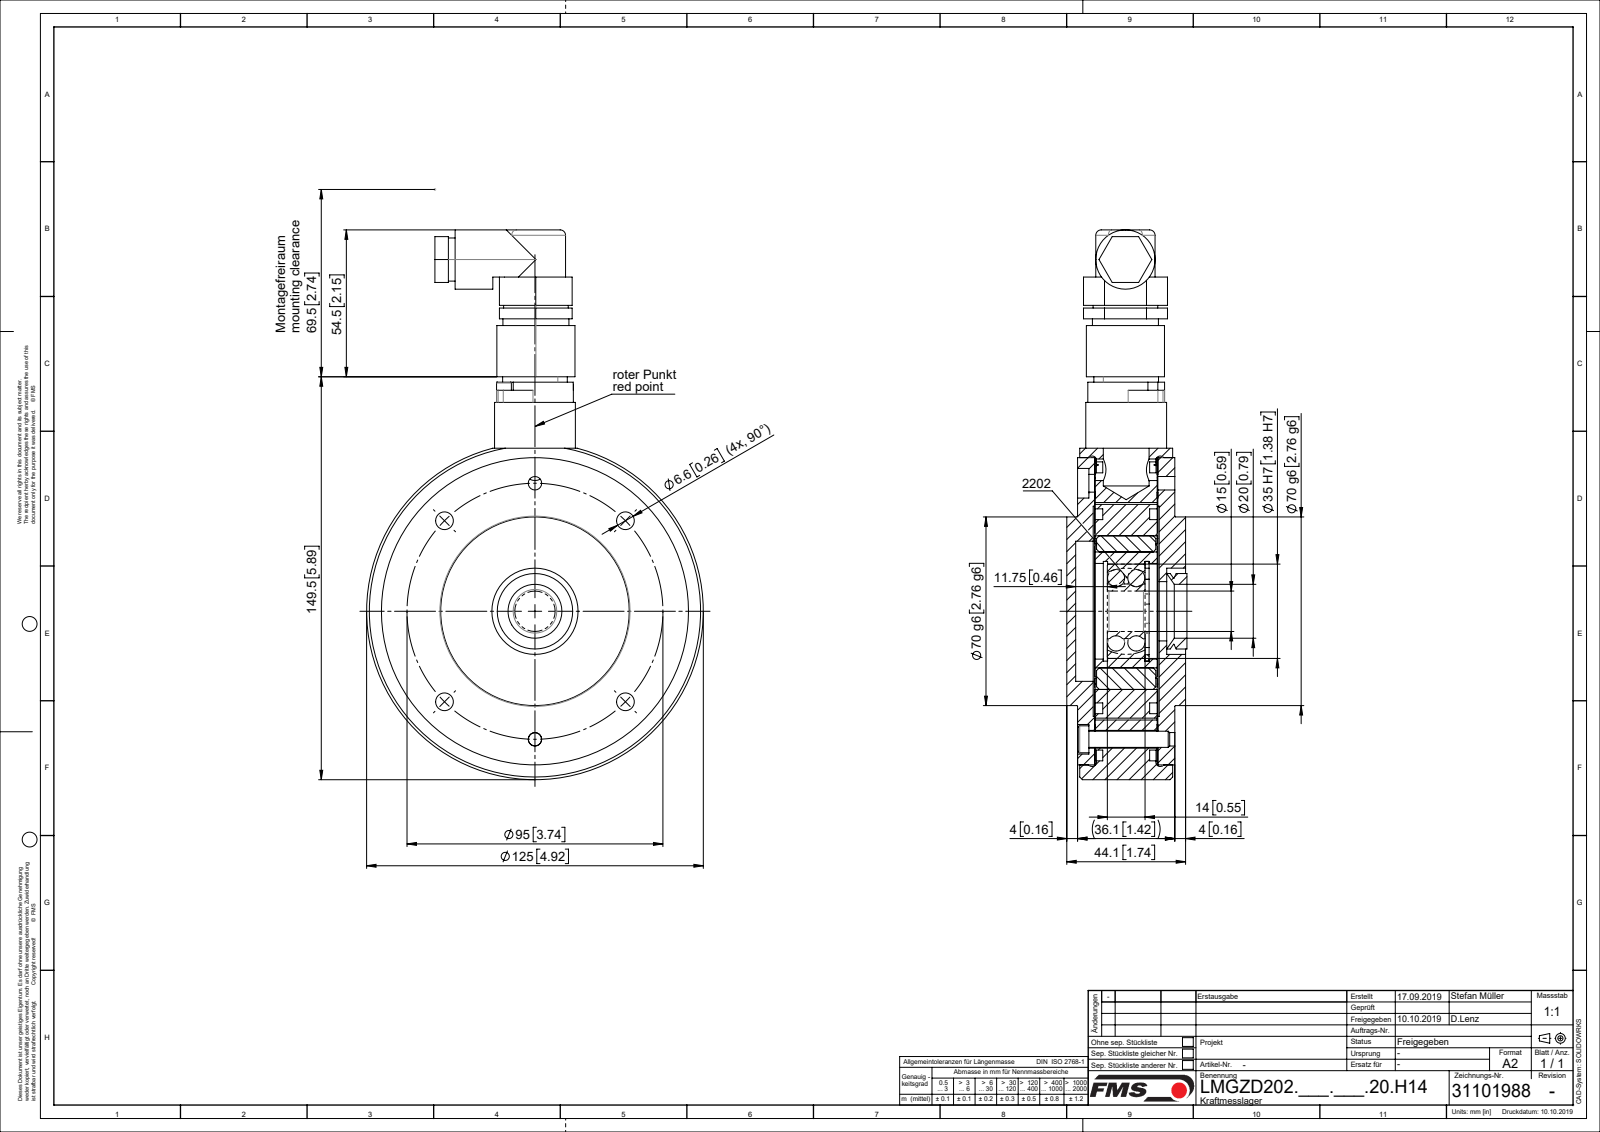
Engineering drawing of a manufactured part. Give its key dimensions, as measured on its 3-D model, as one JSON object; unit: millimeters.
{"part_name": "ZEICHNUNG3; L48996; L4899503; TEIL1 (+8 more)", "step_written_by": "Mechanical Desktop 2009 (CONFIG_CONTROL_DESIGN)", "units": "millimeters", "bodies": {"solids": 14, "faces": 367, "planar": 116, "cylindrical": 218, "other": 33}, "overall_size": [204, 125, 44.1], "volume_mm3": 475453, "surface_area_mm2": 141428, "round_holes": [[6.6, 6], [2.49, 4], [3, 2], [3.6, 2], [5, 2], [11, 2], [22, 2], [14, 1], [15, 1], [20, 1], [22.21, 1], [23.6, 1]], "round_bosses_or_shafts": [[2.15, 7], [5.5, 2], [125, 1], [114, 1], [103, 1], [70, 1], [29, 1], [28.5, 1]], "partial_cylinders_radius": [[5, 8], [2, 2], [3, 2], [40.5, 1], [47, 1]], "face_to_face_distances": [23.25, 6.3, 6.55, 29.55, 29.8, 23, 23.5, 5.8, 24, 0.5], "hole_center_spacings": [47.5, 16.26, 22.47, 23, 36.36, 67.18, 87.77, 0.76]}
